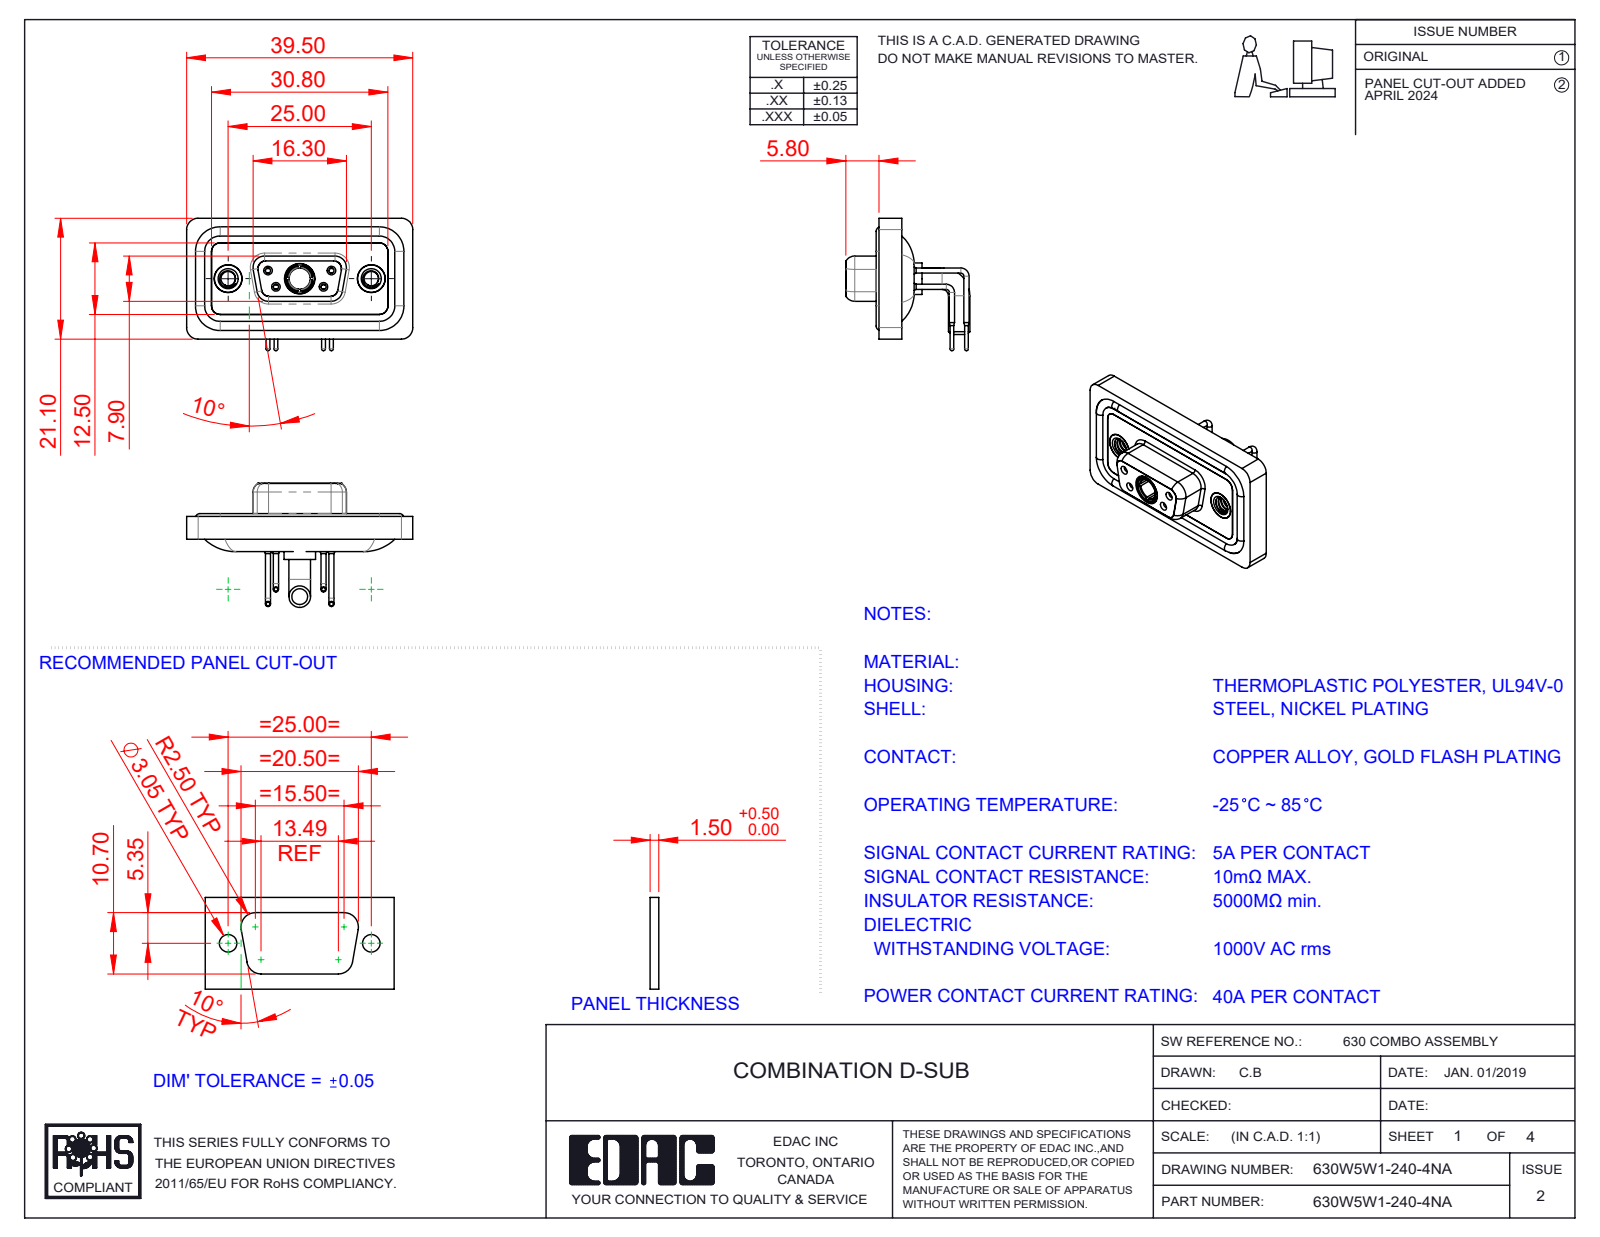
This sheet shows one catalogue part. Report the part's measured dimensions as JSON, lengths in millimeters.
{"part_name": "630Combo Housing_5W1; 630Combo Shell Front_09 Contacts; 630Combo Contact Row 2_50 Contacts; 630Combo Waterproof Housing_09 Contacts (+5 more)", "step_written_by": "SolidWorks 2023 (CONFIG_CONTROL_DESIGN)", "units": "millimeters", "bodies": {"solids": 13, "faces": 670, "planar": 194, "cylindrical": 303, "other": 173}, "overall_size": [39.5, 23.12, 21.68], "volume_mm3": 4894, "surface_area_mm2": 7890, "round_holes": [[0.9, 4], [1.1, 4], [1.5, 4], [2, 4], [4.85, 3], [1.6, 2], [1.7, 2], [2.5, 2], [4, 2], [4.05, 2], [5, 2], [3.7, 1]], "round_bosses_or_shafts": [[1.6, 6], [0.9, 4], [0.65, 4], [4.95, 2], [4.8, 2], [3.75, 2], [5.5, 1], [5.2, 1]], "partial_cylinders_radius": [[1.5, 18], [2, 18], [1.35, 8], [1.6, 8], [0.25, 4], [0.5, 4], [0.6, 4], [0.65, 4]], "face_to_face_distances": [0.4, 1.8, 1.1, 2.9, 2.5, 1.6, 3.1, 2.1, 1.5, 0.5], "hole_center_spacings": [3.16, 5.72, 7.1, 12.5, 18.1, 4.39, 4.4, 8.31]}
